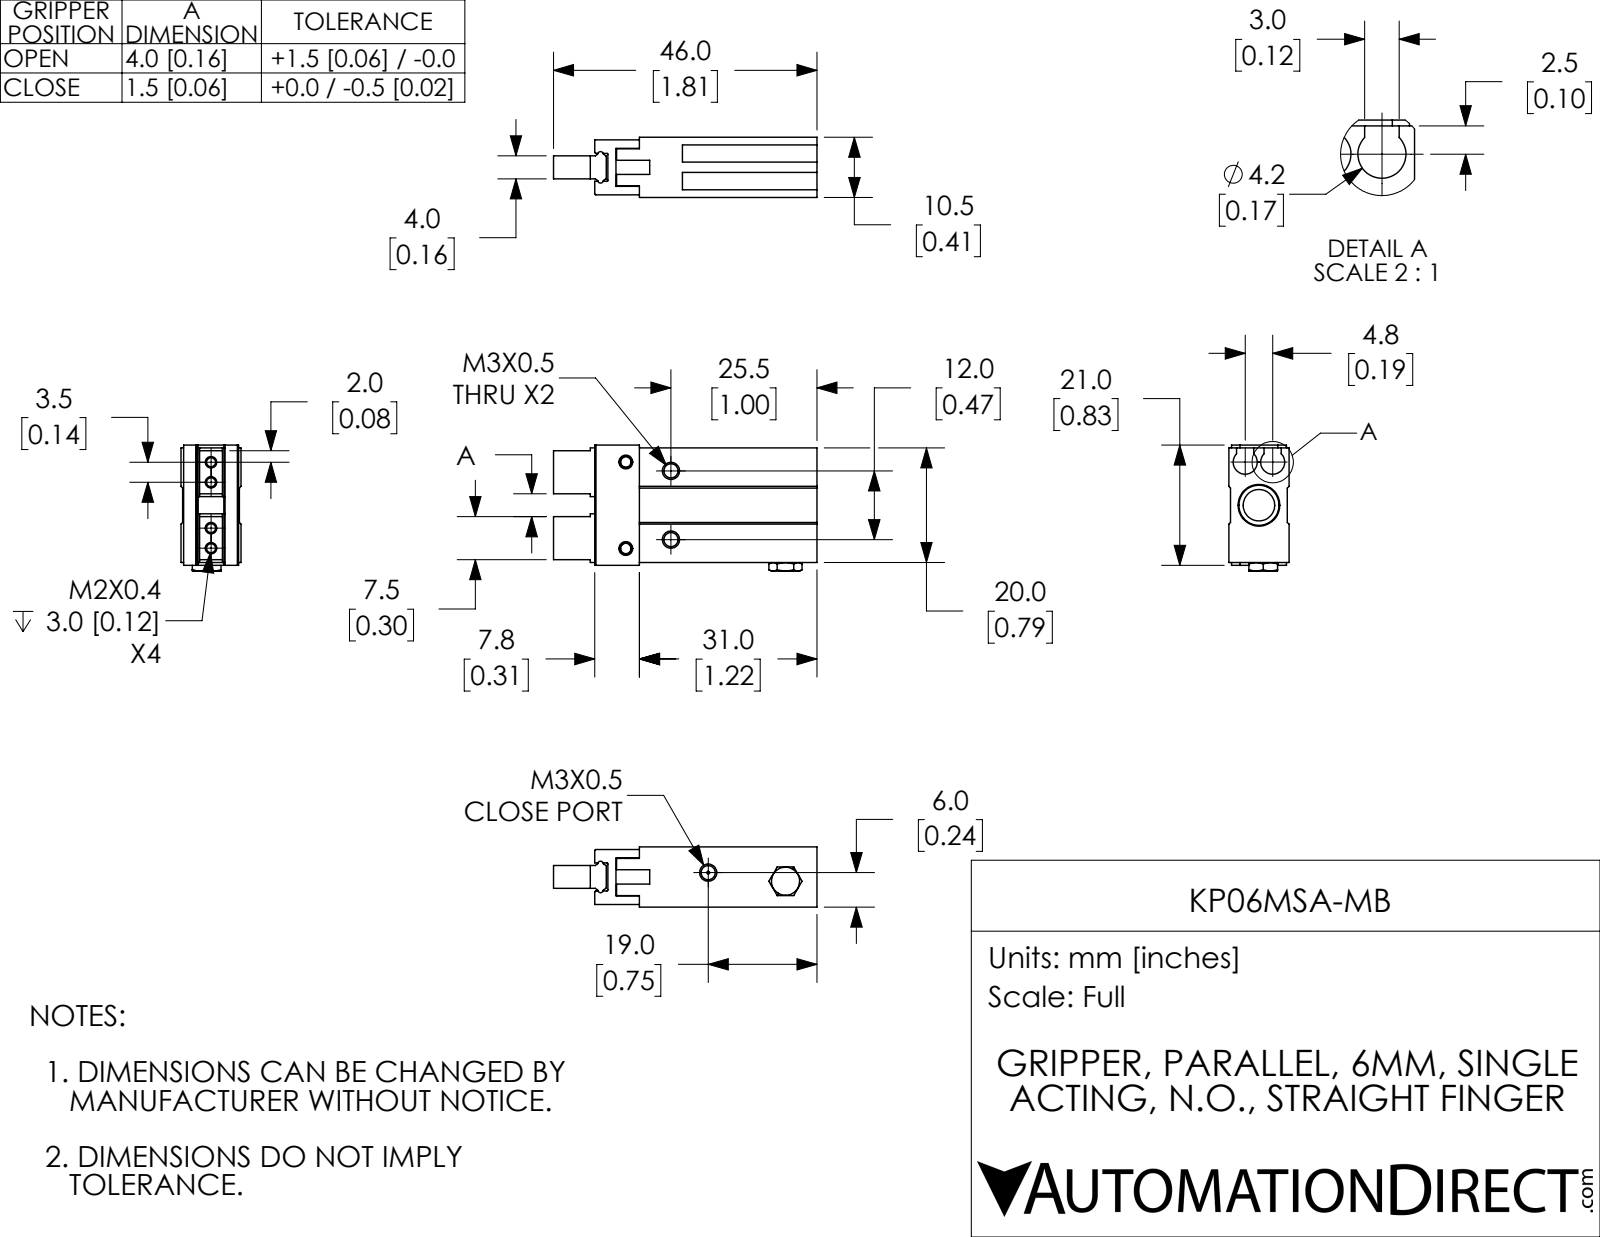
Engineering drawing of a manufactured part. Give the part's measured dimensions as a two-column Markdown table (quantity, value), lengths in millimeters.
| quantity | value |
| --- | --- |
| part name | KP06MSA-MB; KP06MSA-MB-3; KP06MSA-MB-2; KP06MSA-MB-1 |
| STEP written by | SolidWorks 2017 (CONFIG_CONTROL_DESIGN) |
| units | millimeters |
| bodies | 3 solids, 192 faces (106 planar, 44 cylindrical, 42 other) |
| overall size | 46 × 22 × 10.5 |
| volume | 7 013 mm³ |
| surface area | 5 094 mm² |
| round holes (diameter × count) | 2.46 × 3, 0.5 × 2, 3.1 × 2, 2.46 × 1, 5.5 × 1, 7 × 1 |
| partial cylindrical surfaces (radius × count) | 0.2 × 4, 0.78 × 4, 0.78 × 4, 0.5 × 2, 2.1 × 2 |
| main face-to-face distances | 3.25, 2, 4, 10.5, 3.7, 10.2, 0.45, 6.5, 10.05, 9.75 |
| hole center spacings | 12, 13.58 |
